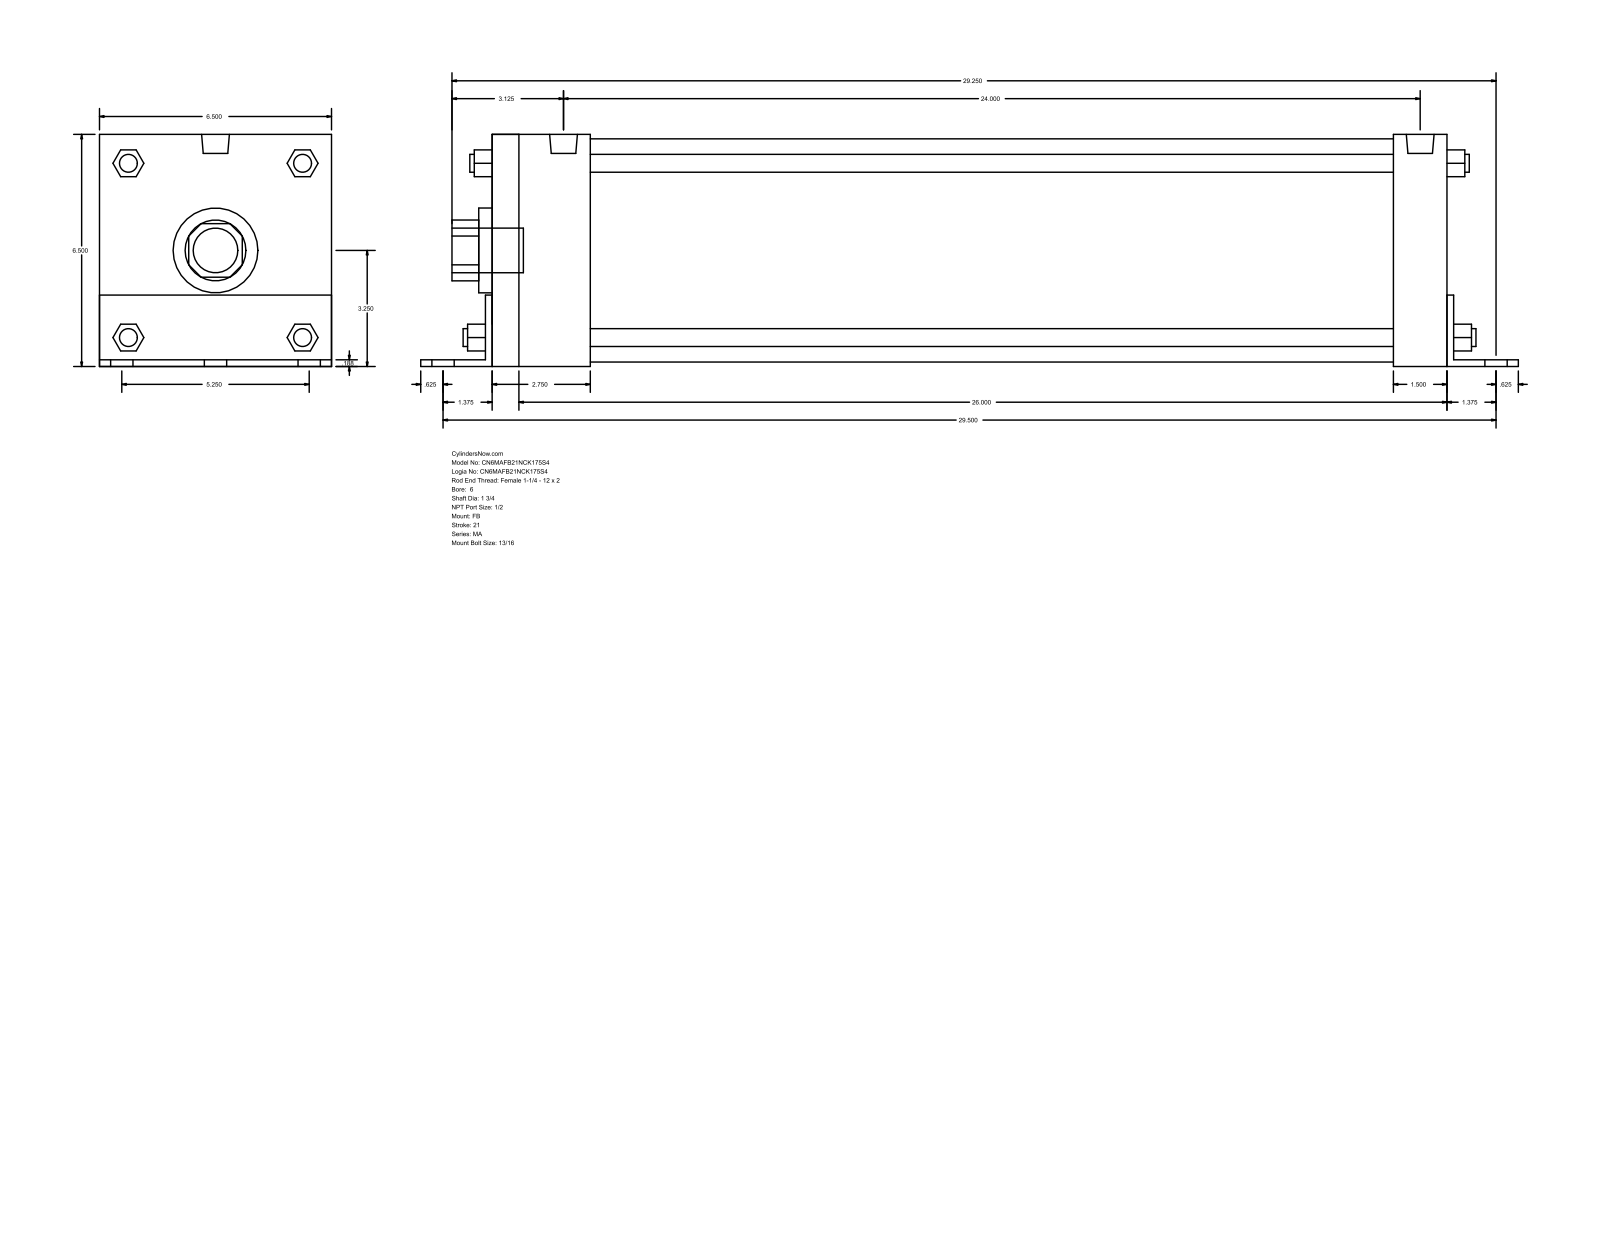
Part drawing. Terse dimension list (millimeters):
name: MA_FB__0600_1.75
written by: GSSL Pune (CONFIG_CONTROL_DESIGN)
unit: mm
bodies: 0 solids, 140 faces (105 planar, 35 cylindrical, 0 other)
size: 781.05 × 165.15 × 165.1
holes: 1× ⌀44.45, 1× ⌀60.33, 1× ⌀158.75
bosses: 6× ⌀20.64, 4× ⌀17.46, 4× ⌀12.7, 2× ⌀19.77, 1× ⌀31.75
rounds: 1× R21.63, 1× R32.05
face distances: 165.1, 4.76, 679.45, 165.15, 4.71, 160.39, 38.1, 4.77, 684.22, 684.21
